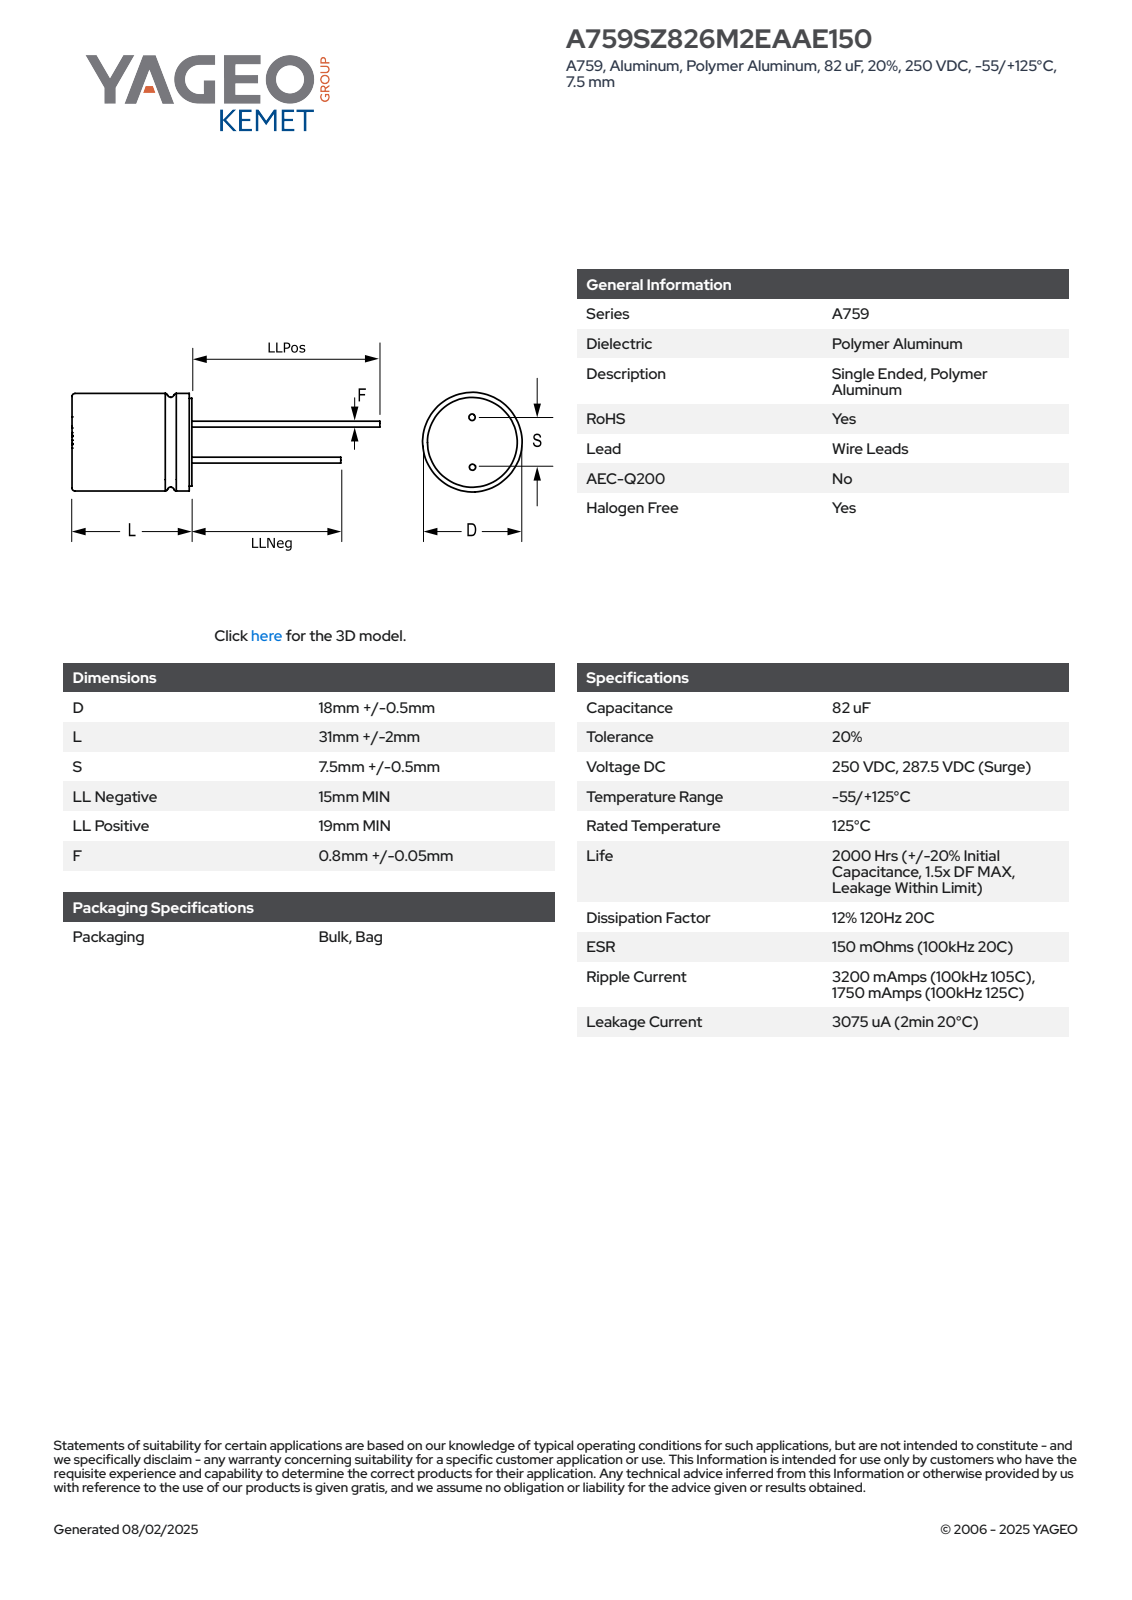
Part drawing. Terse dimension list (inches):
name: CAR_KP_18X31_D18.5L33S7.5F0.85
written by: SolidWorks 2014 (AUTOMOTIVE_DESIGN)
unit: in
bodies: 4 solids, 75 faces (61 planar, 8 cylindrical, 6 other)
size: 2.048 × 0.728 × 0.728
volume: 0.537 in³; area: 4.063 in²
bosses: 2× ⌀0.033, 1× ⌀0.728
face distances: 1.299, 1.3, 1.89, 2.048, 1.89, 2.047, 0.591, 0.748, 0.157, 0.08
